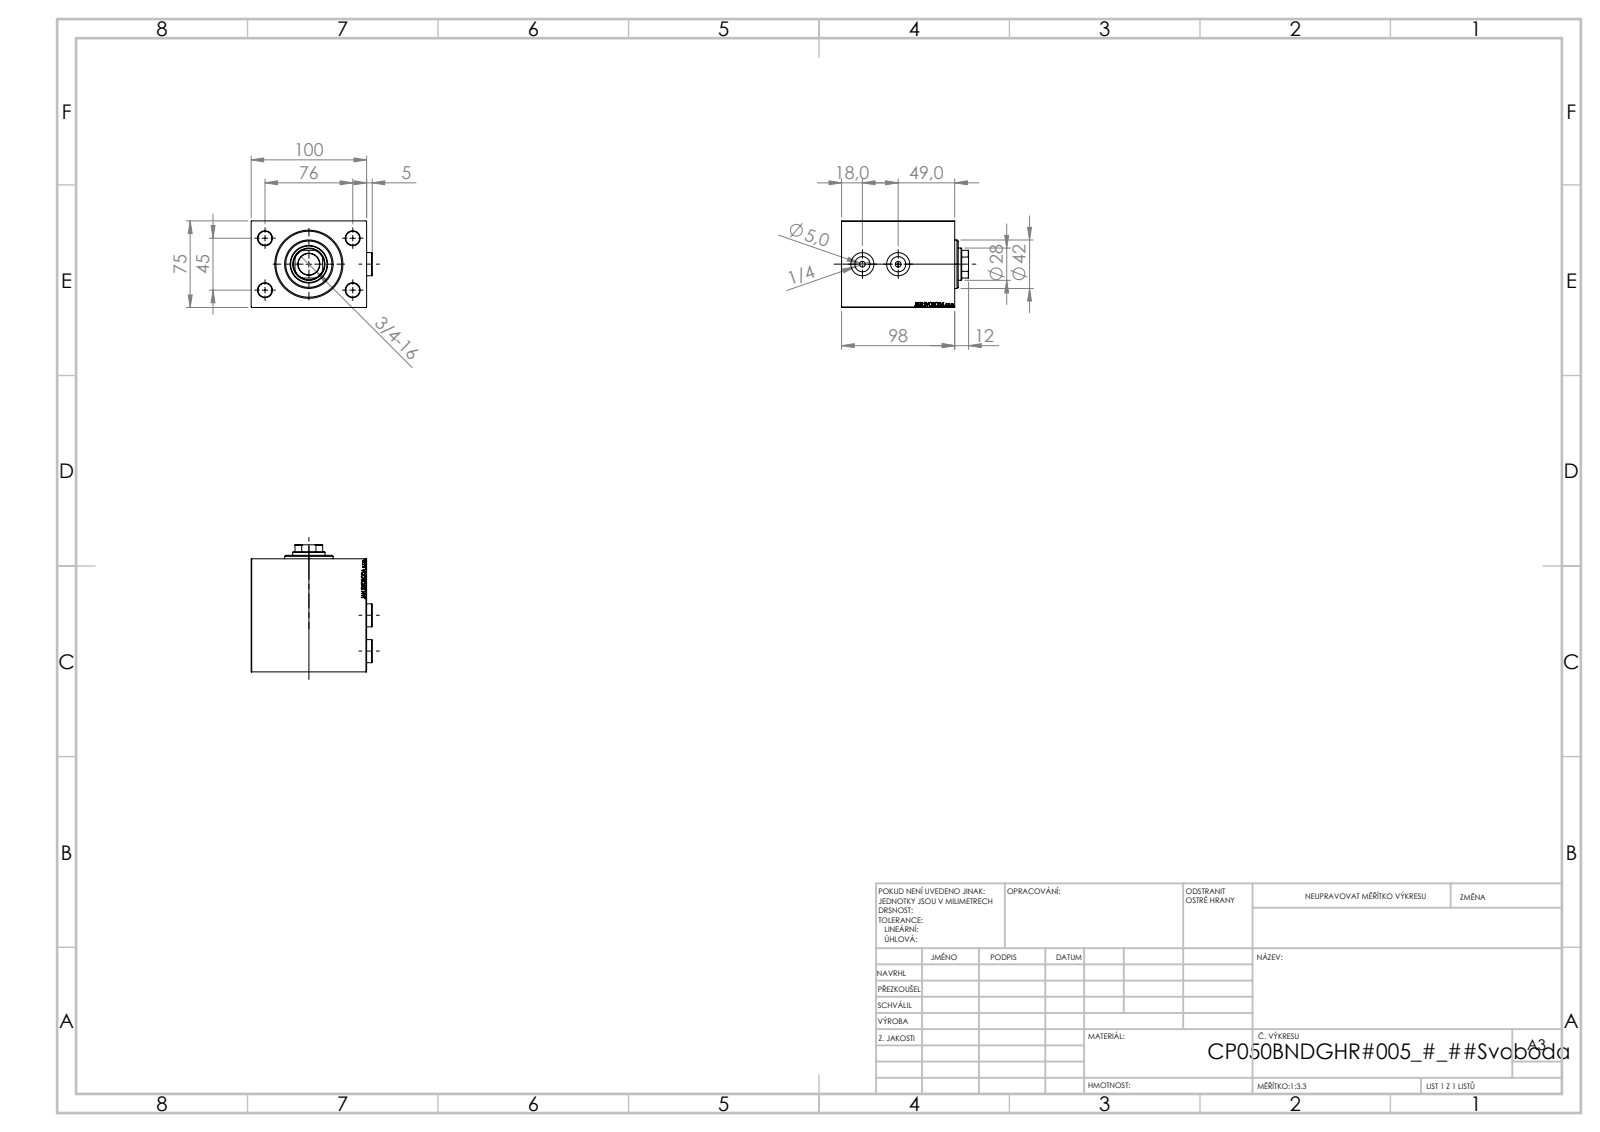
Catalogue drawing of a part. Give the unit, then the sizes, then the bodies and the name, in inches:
Units: inches
Overall size (bounding box): 4.331 × 4.13 × 2.953
Round holes (diameter × count): ⌀0.472 ×4, ⌀0.157 ×2, ⌀0.197 ×2, ⌀0.383 ×2, ⌀0.518 ×2, ⌀0.591 ×2, ⌀0.787 ×2, ⌀0.728 ×1, ⌀1.102 ×1, ⌀1.24 ×1, ⌀1.28 ×1, ⌀1.969 ×1
Round bosses / shafts (diameter × count): ⌀1.654 ×1
Partial cylindrical surfaces — rounded edges, fillets, slot ends (radius × count): R0.531 ×1
Main face-to-face distances: 2.953, 3.937, 3.858, 1.929, 0.551, 3.307, 0.197, 1.732, 1.378, 2.126
Hole centre spacings: 1.739, 1.772, 2.992, 3.477, 1.22, 1.675
Volume: 42.94 in³ · Surface area: 165.8 in²
Bodies: 5 solids, 959 faces (441 planar, 84 cylindrical, 434 other)
Part name (STEP PRODUCT): V450CP_B; V450CP_B_VCP; PLUG; V450CP_VC_B
STEP written by: SolidWorks 2019 (CONFIG_CONTROL_DESIGN)
